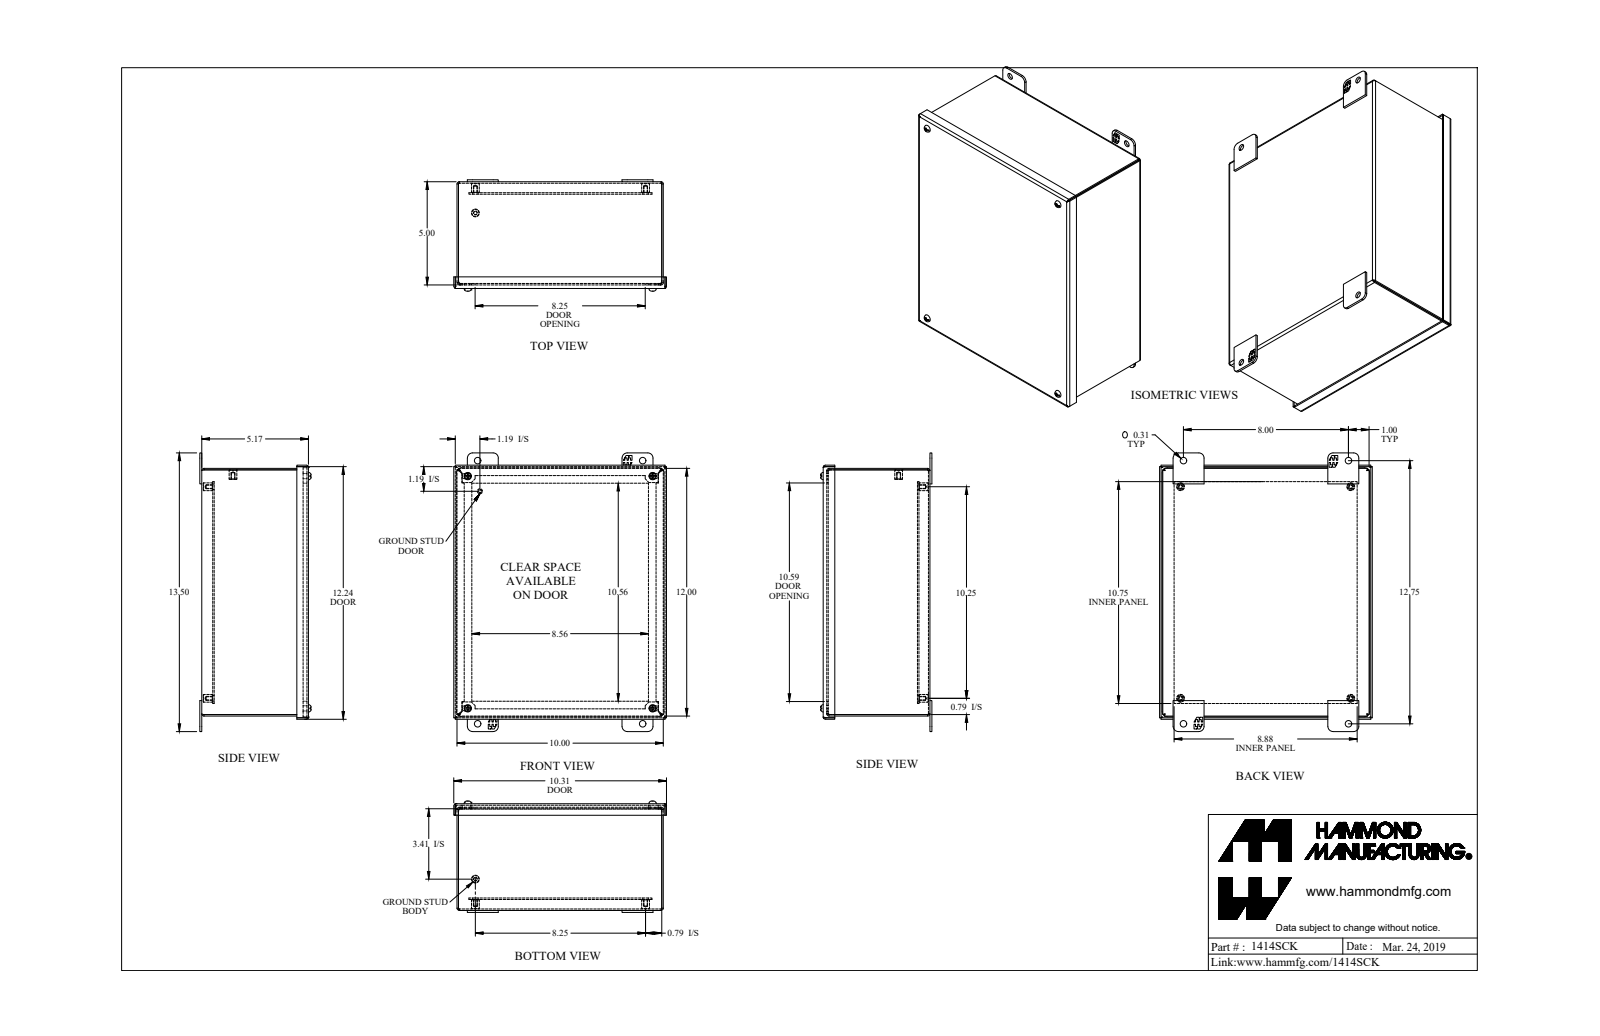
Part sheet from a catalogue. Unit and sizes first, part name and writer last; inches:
Units: inches
Overall size (bounding box): 13.5 × 10.312 × 5.394
Round holes (diameter × count): ⌀0.156 ×5, ⌀0.159 ×4, ⌀0.25 ×4, ⌀0.265 ×4, ⌀0.312 ×4
Round bosses / shafts (diameter × count): ⌀0.375 ×5, ⌀0.39 ×4, ⌀0.275 ×4, ⌀0.19 ×4, ⌀0.148 ×4, ⌀0.25 ×1, ⌀0.188 ×1
Partial cylindrical surfaces — rounded edges, fillets, slot ends (radius × count): R0.25 ×12, R0.007 ×8, R0.036 ×8, R0.079 ×8, R0.108 ×8, R0.125 ×8, R0.281 ×8, R0.16 ×4
Main face-to-face distances: 0.072, 5.1, 4.568, 0.532, 5.172, 5.028, 9.928, 4.64, 0.46, 4.496
Hole centre spacings: 8.513, 0.89, 12.011, 14.695, 8, 8.25, 8.605, 8.956
Volume: 49.24 in³ · Surface area: 1 297 in²
Bodies: 30 solids, 706 faces (474 planar, 172 cylindrical, 60 other)
Part name (STEP PRODUCT): 1414SCK
STEP written by: SolidWorks 2019 (AUTOMOTIVE_DESIGN)
